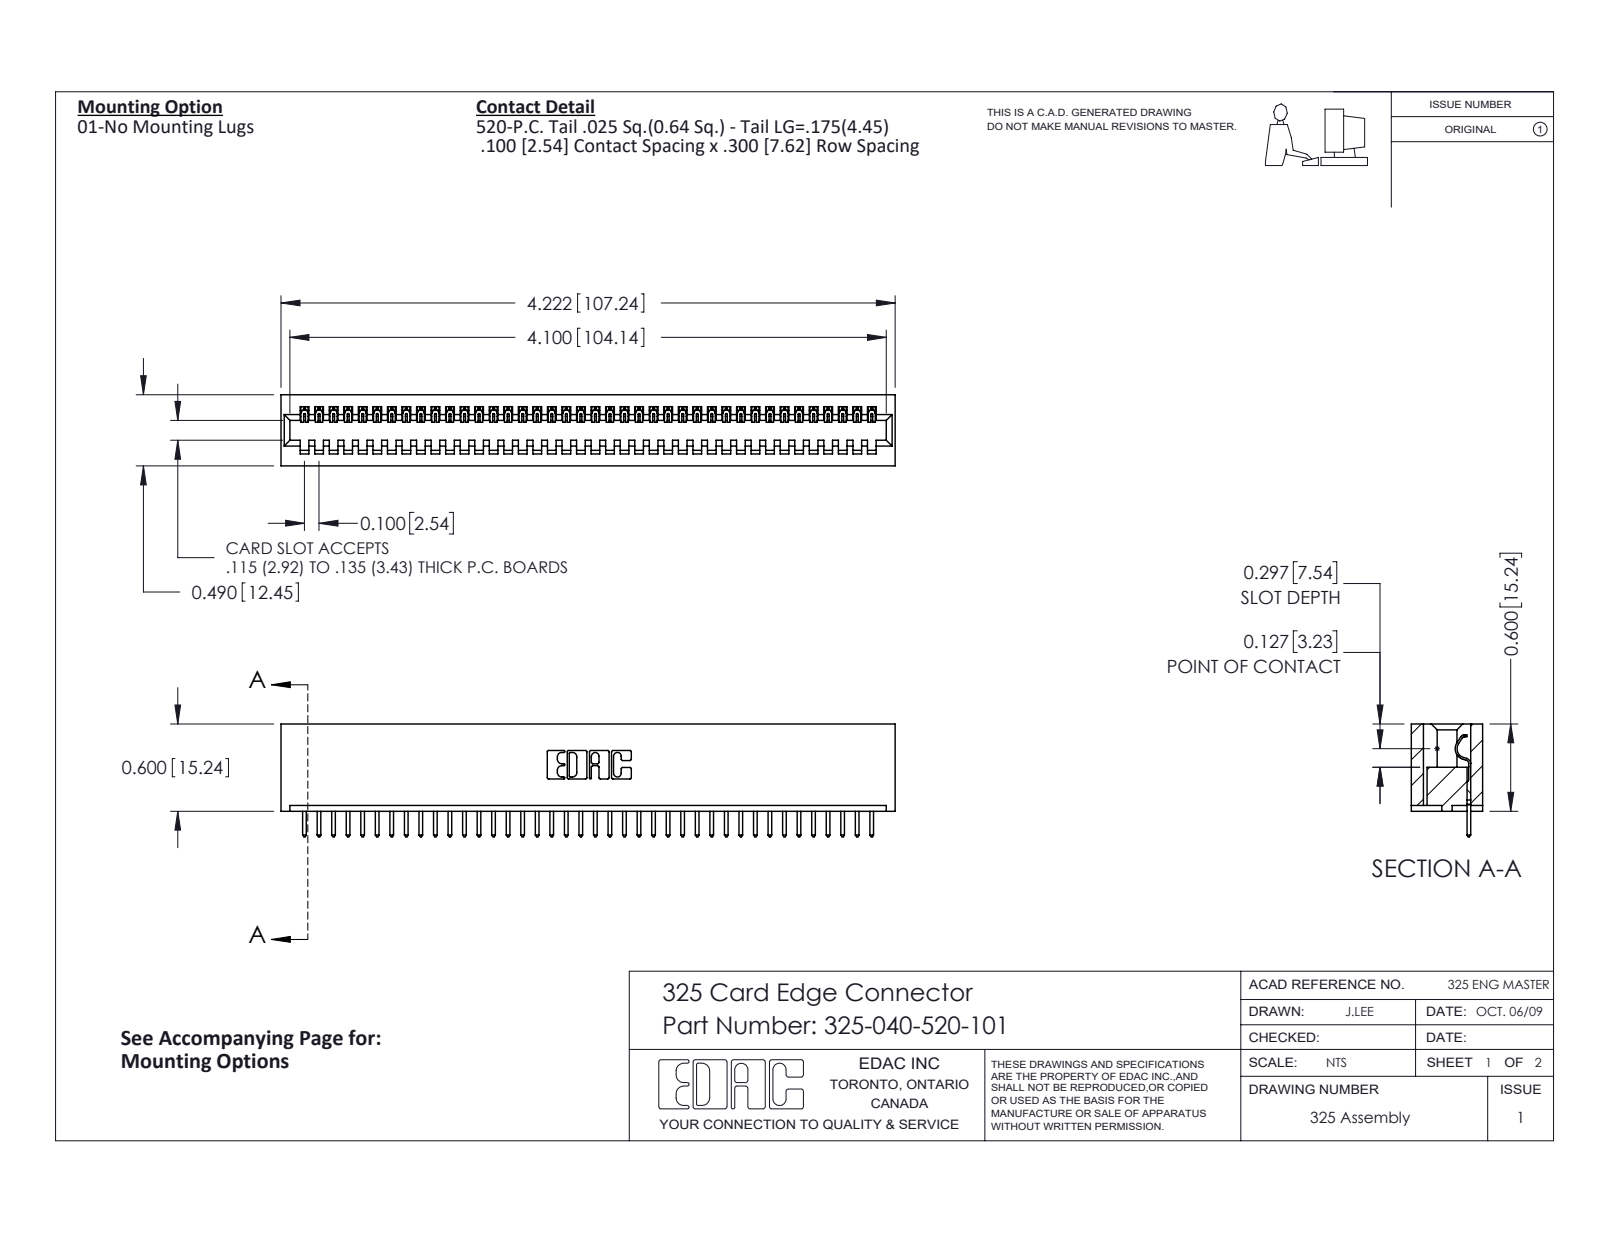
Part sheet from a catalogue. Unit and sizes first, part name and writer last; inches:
Units: inches
Overall size (bounding box): 4.222 × 0.775 × 0.49
Partial cylindrical surfaces — rounded edges, fillets, slot ends (radius × count): R0.006 ×80, R0.01 ×80, R0.01 ×22, R0.007 ×6, R0.031 ×6, R0.026 ×3, R0.014 ×1, R0.022 ×1
Main face-to-face distances: 0.083, 0.407, 0.49, 0.3, 0.107, 0.383, 0.025, 0.325, 0.56, 0.263
Volume: 0.858 in³ · Surface area: 23.88 in²
Bodies: 41 solids, 2426 faces (1746 planar, 680 cylindrical, 0 other)
Part name (STEP PRODUCT): 325-040-520-101; 325-292-001_325-293-120; 325 Part_Lugless
STEP written by: SolidWorks 2016 (CONFIG_CONTROL_DESIGN)
